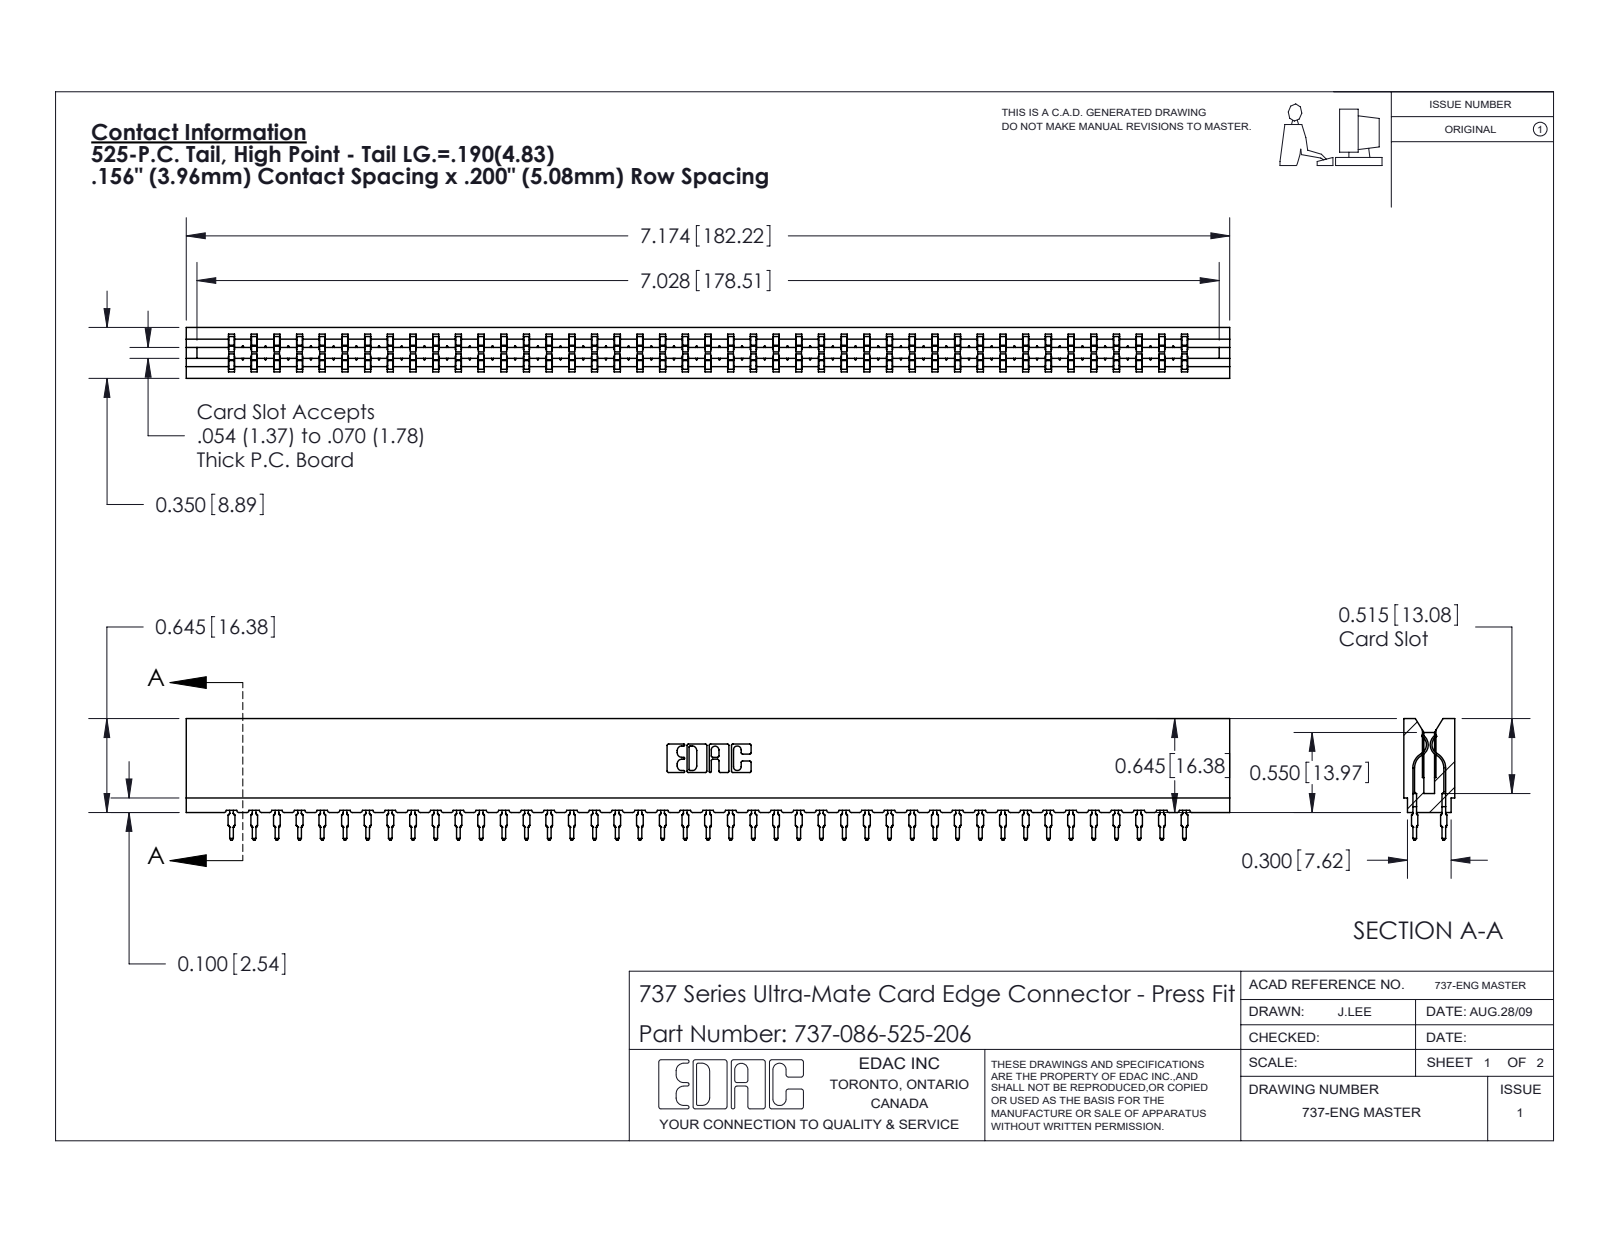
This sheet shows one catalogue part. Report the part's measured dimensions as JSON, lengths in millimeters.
{"part_name": "737 Part_Insulator Option - 06; 745-292-001_525; 737-086-525-206", "step_written_by": "SolidWorks 2020 (CONFIG_CONTROL_DESIGN)", "units": "millimeters", "bodies": {"solids": 87, "faces": 7835, "planar": 4054, "cylindrical": 1545, "other": 2236}, "overall_size": [182.2, 21.2, 8.9], "volume_mm3": 17960, "surface_area_mm2": 26030, "partial_cylinders_radius": [[0.5, 172], [0.4, 86], [0.3, 22], [0.1, 8], [0.3, 8], [0.2, 6], [0.8, 6], [0.7, 3]], "face_to_face_distances": [3.5, 5.4, 8.9, 1.6, 7.3, 1.9, 3.8, 1.9, 1.1, 7.7]}
